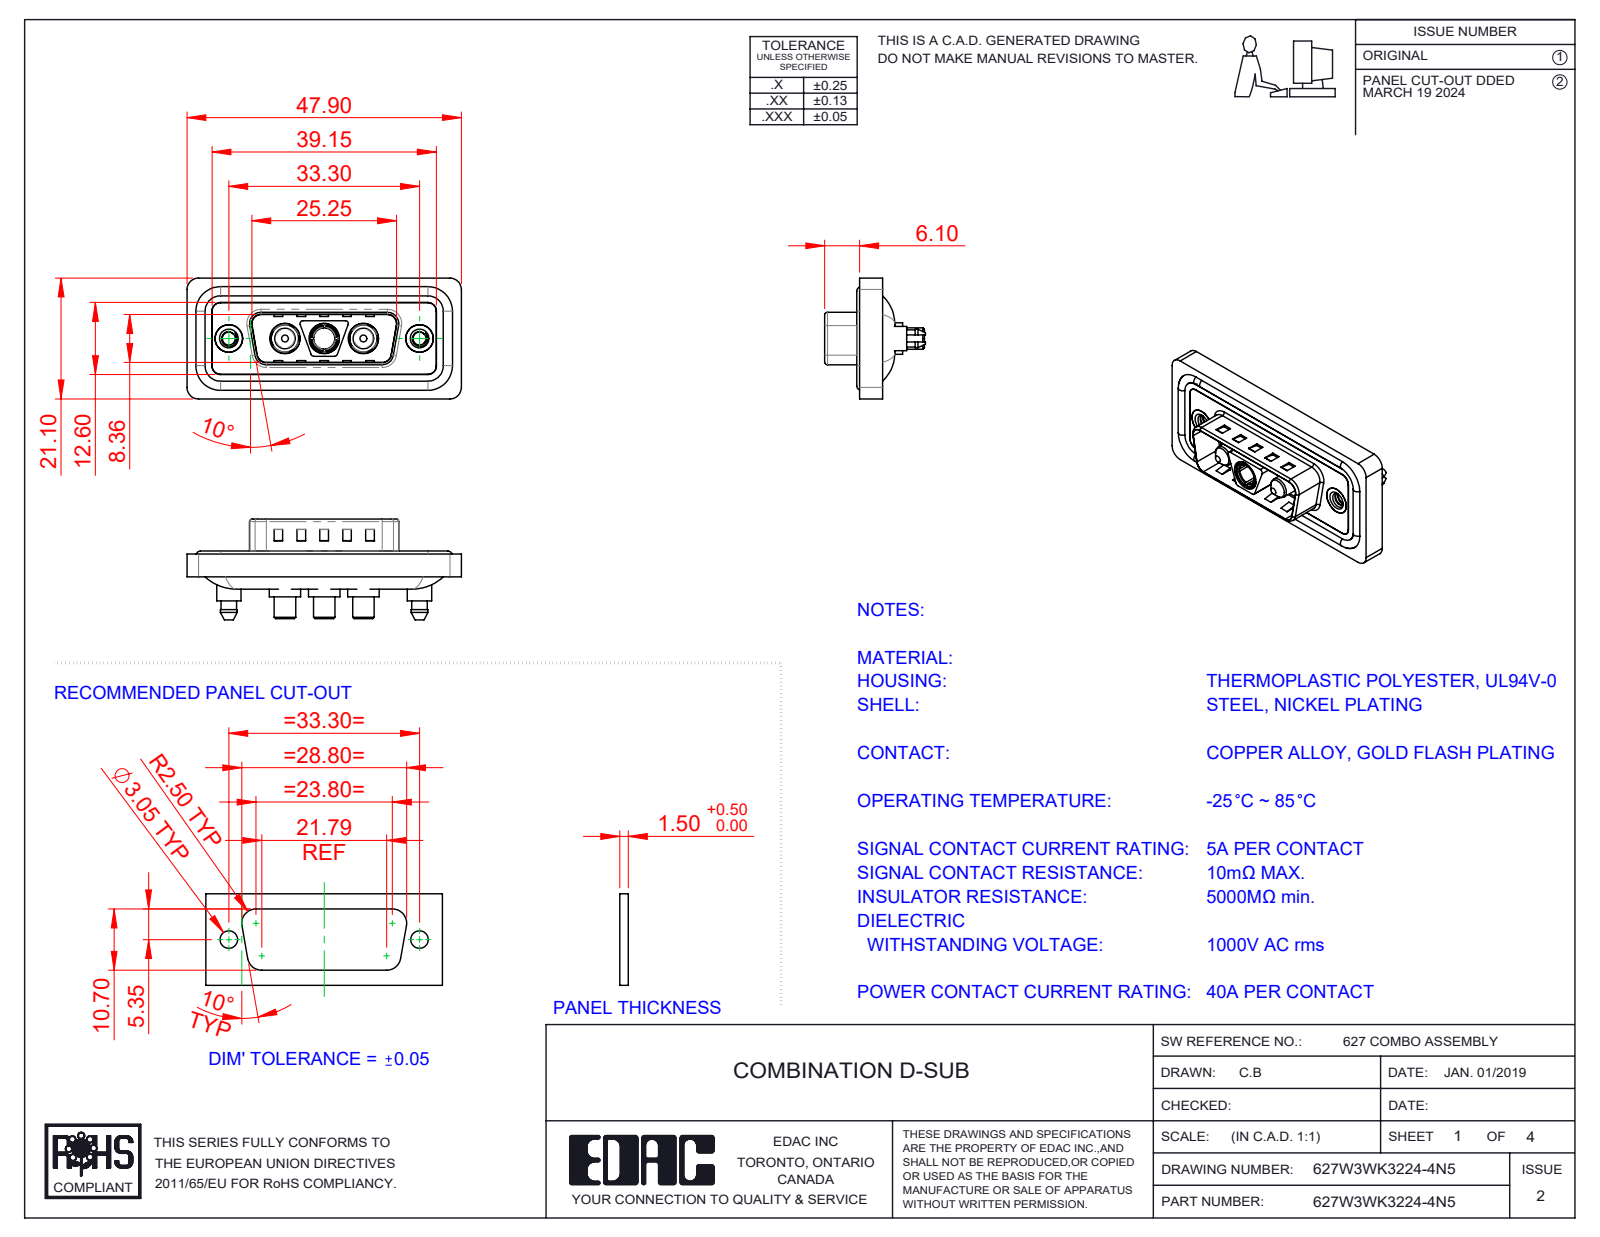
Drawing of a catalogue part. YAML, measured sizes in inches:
part_name: "627W3WK3224-4N5; 627Combo Waterproof Housing_15 Contacts; 627Combo Shell Rear_15 Contacts; Power Pin_40A S (+4 more)"
step_written_by: "SolidWorks 2023 (CONFIG_CONTROL_DESIGN)"
units: inches
bodies: {solids: 13, faces: 659, planar: 247, cylindrical: 282, other: 130}
overall_size: [1.886, 0.831, 0.693]
volume: 0.359
surface_area: 14.71
round_holes:
  - {diameter: 0.191, count: 3}
  - {diameter: 0.209, count: 3}
  - {diameter: 0.089, count: 2}
  - {diameter: 0.157, count: 2}
  - {diameter: 0.189, count: 2}
  - {diameter: 0.197, count: 2}
  - {diameter: 0.146, count: 1}
round_bosses_or_shafts:
  - {diameter: 0.063, count: 4}
  - {diameter: 0.217, count: 3}
  - {diameter: 0.205, count: 3}
  - {diameter: 0.187, count: 3}
  - {diameter: 0.148, count: 3}
  - {diameter: 0.213, count: 2}
  - {diameter: 0.193, count: 2}
  - {diameter: 0.167, count: 2}
partial_cylinders:
  - {radius: 0.059, count: 28}
  - {radius: 0.079, count: 20}
  - {radius: 0.02, count: 12}
  - {radius: 0.063, count: 10}
  - {radius: 0.01, count: 4}
  - {radius: 0.024, count: 4}
  - {radius: 0.026, count: 4}
  - {radius: 0.035, count: 4}
face_to_face_distances: [0.016, 0.043, 0.059, 0.122, 0.02, 0.063, 0.114, 0.157, 0.028, 0.032]
hole_center_spacings: [0.27, 0.386, 0.656, 0.925, 0.539, 1.311]
